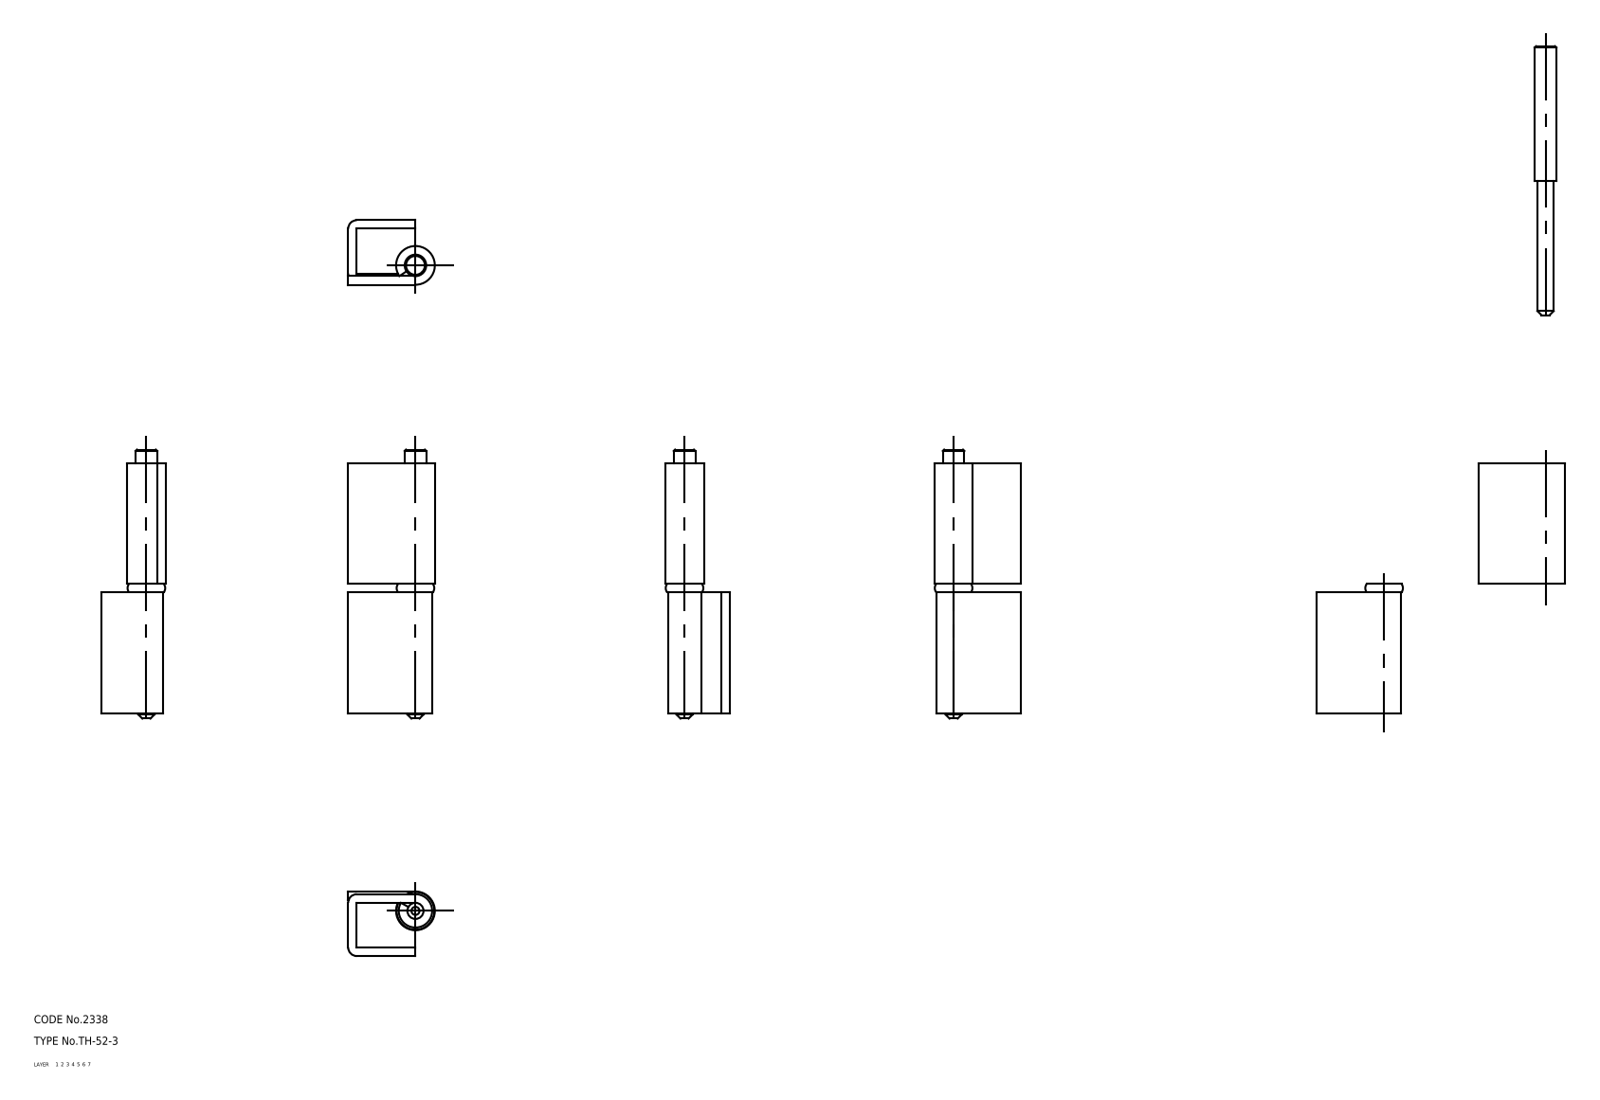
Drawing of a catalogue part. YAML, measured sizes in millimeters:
part_name: "washer; shaft; hinge piece_B; hinge piece_A (+1 more)"
step_written_by: "CADfix (AUTOMOTIVE_DESIGN)"
units: millimeters
bodies: {solids: 4, faces: 39, planar: 0, cylindrical: 0, other: 39}
overall_size: [100, 32.2, 24]
volume: 24983
surface_area: 17118
